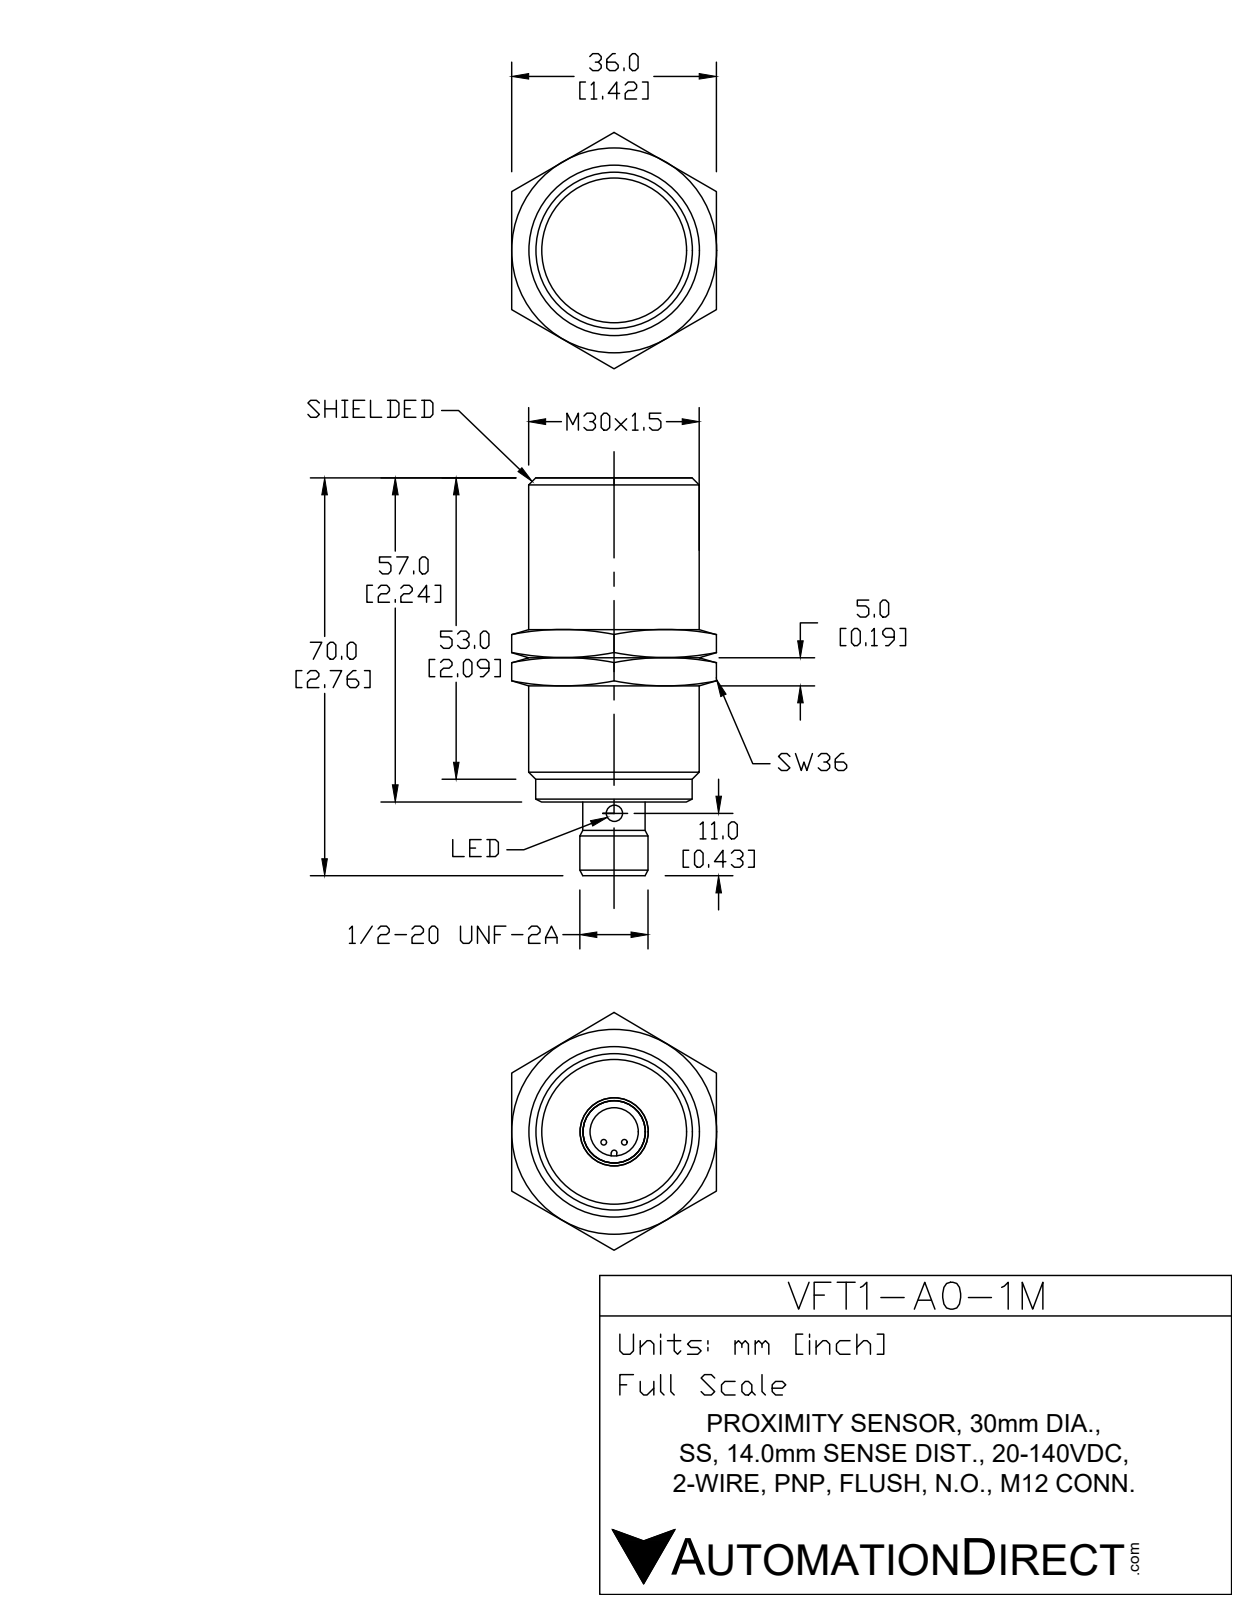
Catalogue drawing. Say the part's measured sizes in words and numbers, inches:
The part is named "VFT1-A0-1M". Its 3-D file was written by "SolidWorks 2017 (AUTOMOTIVE_DESIGN)". It is 3 solids with 102 faces: 28 planar, 44 cylindrical and 30 other. Overall it measures 2.756 by 1.637 by 1.417 inches. Its volume is 2.776 cubic inches and its surface area 17.32 square inches. Round holes: 1 of diameter 0.098, 1 of diameter 0.118, 1 of diameter 0.299, 1 of diameter 1.117. Round bosses or shafts: 1 of diameter 1.181, 1 of diameter 1.094, 1 of diameter 1.075, 1 of diameter 1.059, 1 of diameter 0.5, 1 of diameter 0.445, 1 of diameter 0.417. Partial cylindrical surfaces (rounded edges, fillets, slot ends): 8 of radius 0.008, 1 of radius 0.173, 1 of radius 0.197. The main face-to-face distances are 0.197, 1.417, 1.102, 1.142, 2.244, 1.339, 0.906, 0.945, 0.394, 1.299.
